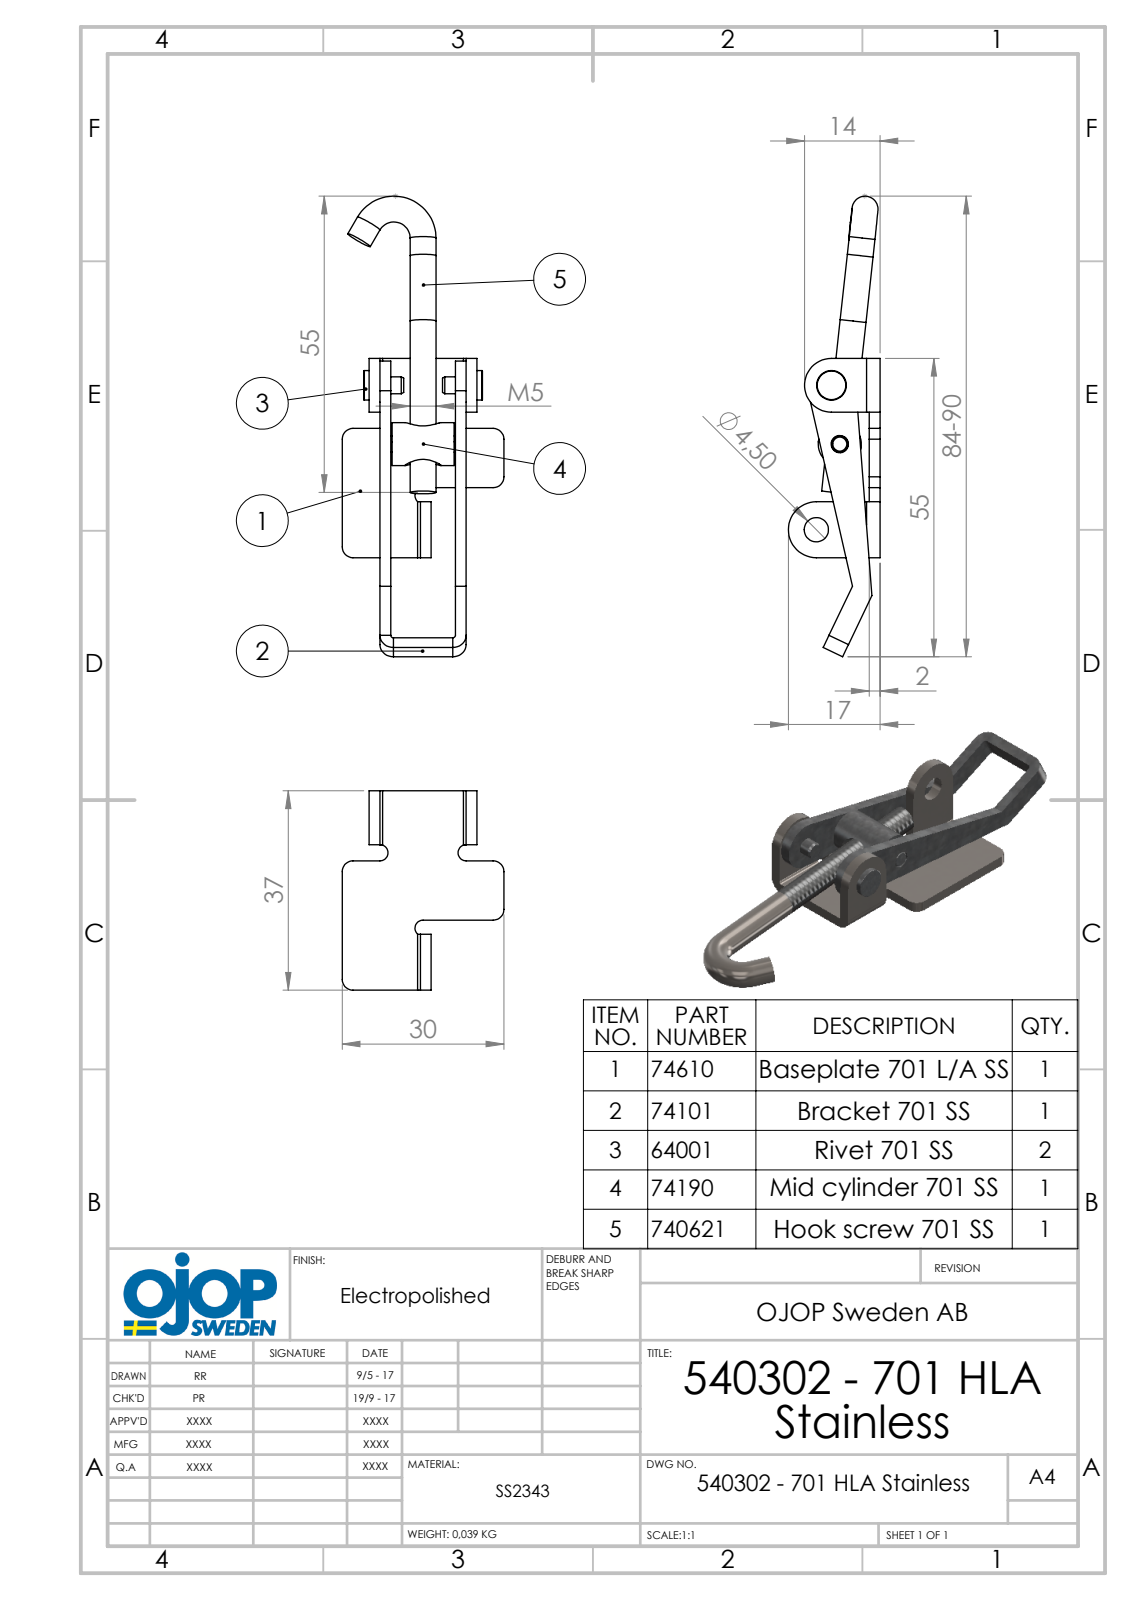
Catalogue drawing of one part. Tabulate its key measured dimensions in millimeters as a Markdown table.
| quantity | value |
| --- | --- |
| part name | 701 - Bygel; 701 - Ansatsnit; 701 - Mid Cylinder; Hake M5 (+2 more) |
| STEP written by | SolidWorks 2015 (AUTOMOTIVE_DESIGN) |
| units | millimeters |
| bodies | 6 solids, 147 faces (62 planar, 67 cylindrical, 18 other) |
| overall size | 85.51 × 30 × 17 |
| volume | 5 275 mm³ |
| surface area | 6 318 mm² |
| round holes (diameter × count) | 3.2 × 2, 4.5 × 2, 4.8 × 1 |
| round bosses / shafts (diameter × count) | 4.8 × 2, 8 × 1, 5.5 × 1, 4.81 × 1, 3.15 × 1, 3 × 1 |
| partial cylindrical surfaces (radius × count) | 0.5 × 5, 2.5 × 5, 2 × 4, 1.5 × 3, 4.5 × 1, 5 × 1, 5.19 × 1 |
| main face-to-face distances | 2, 14, 16, 4, 12, 6.5, 7.5, 9.5, 8.5, 18 |
| hole center spacings | 11.02, 16.47, 26.95 |
